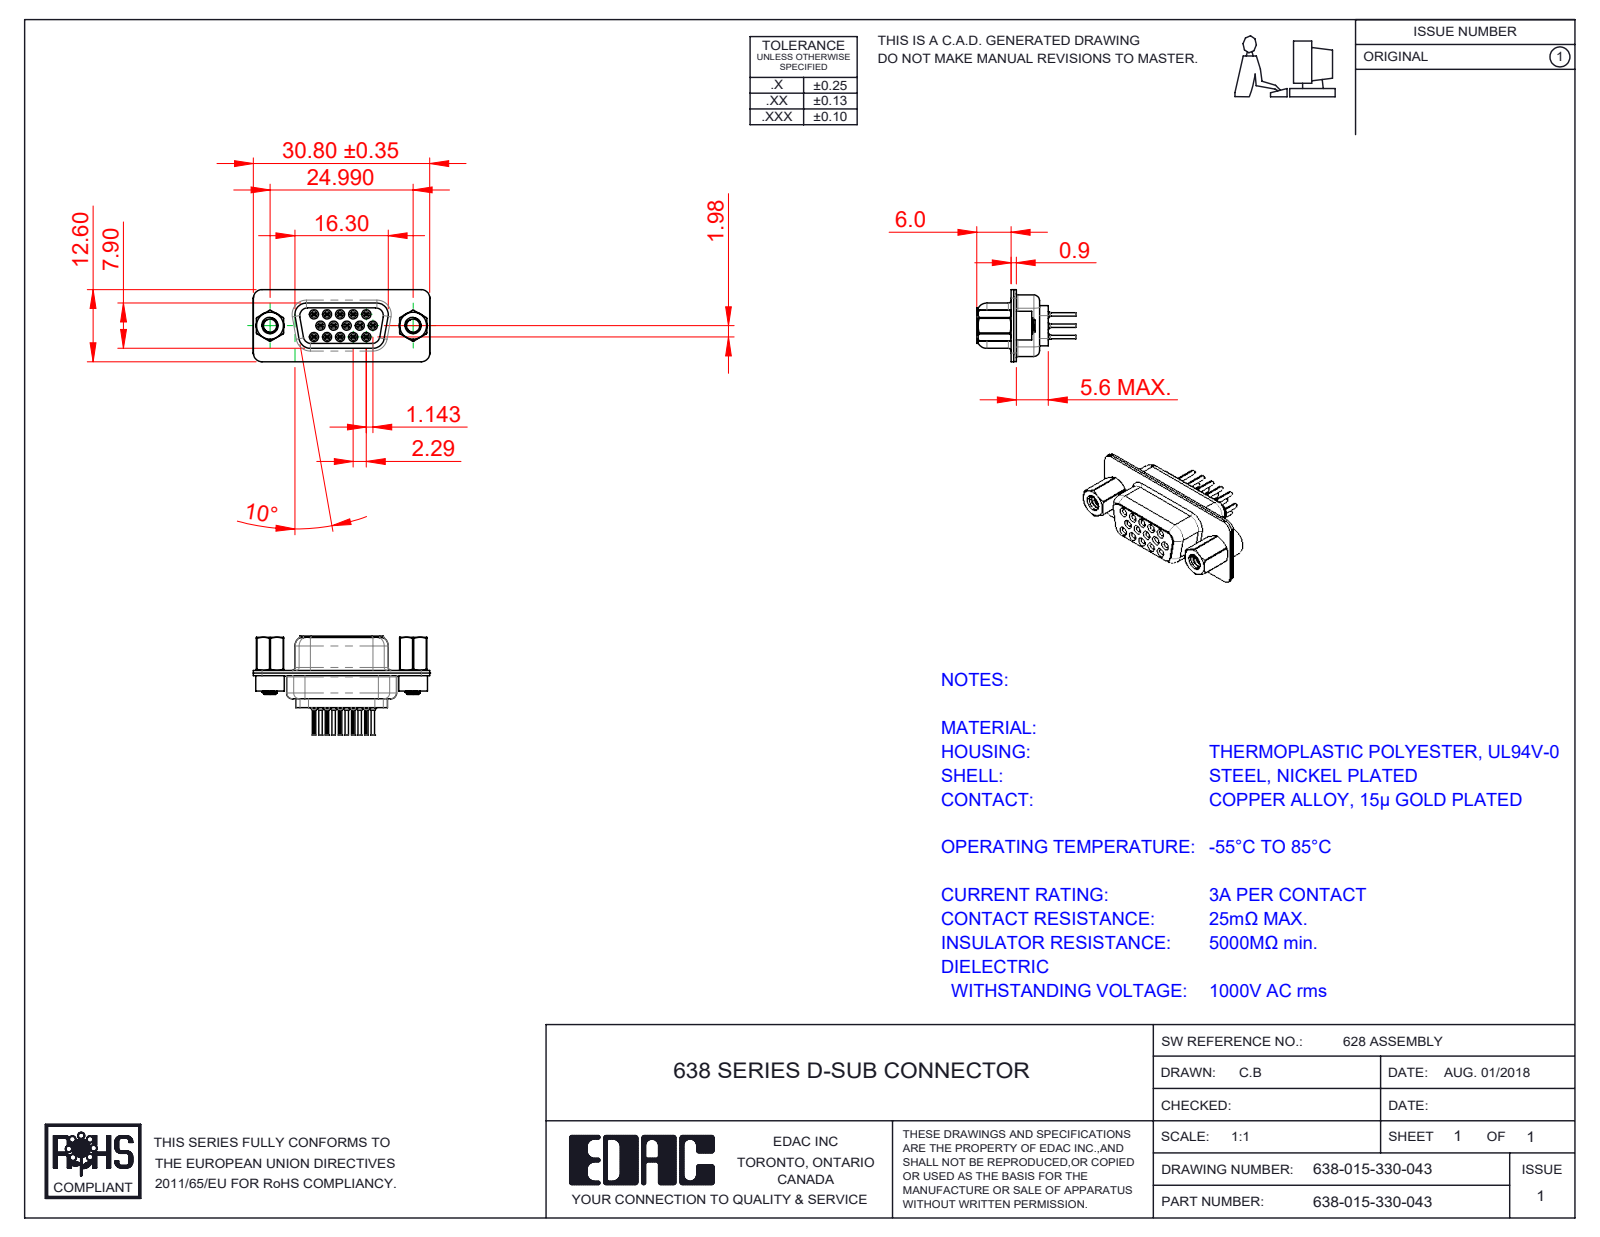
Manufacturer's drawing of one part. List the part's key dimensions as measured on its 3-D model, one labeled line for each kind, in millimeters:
Part name (STEP PRODUCT): 638 4-40 Hex Standoff; 638-015-330-043; 638 Housing_15 Contacts; 638 Contact Row 1_30 (+5 more)
STEP written by: SolidWorks 2020 (CONFIG_CONTROL_DESIGN)
Units: millimetres
Bodies: 22 solids, 2310 faces (554 planar, 704 cylindrical, 1052 other)
Overall size (bounding box): 30.81 × 17.3 × 12.6
Volume: 1 789 mm³ · Surface area: 6 081 mm²
Round holes (diameter × count): ⌀0.2 ×15, ⌀0.8 ×15, ⌀1 ×15, ⌀1.1 ×15, ⌀1.6 ×15, ⌀1.7 ×15, ⌀1.8 ×15, ⌀2 ×2, ⌀2.26 ×2, ⌀2.29 ×2, ⌀4 ×2, ⌀4.05 ×2
Round bosses / shafts (diameter × count): ⌀2 ×15, ⌀1.5 ×15, ⌀1.2 ×15, ⌀0.6 ×15, ⌀5 ×2, ⌀4.95 ×2, ⌀4.8 ×2, ⌀2.79 ×2
Partial cylindrical surfaces — rounded edges, fillets, slot ends (radius × count): R0.1 ×30, R1.5 ×20, R2 ×12, R0.28 ×10, R1.55 ×8, R1.35 ×5, R0.25 ×4, R0.5 ×4
Main face-to-face distances: 0.45, 0.9, 0.4, 1.43, 8.88, 6.6, 1.4, 2.28, 6.2, 0.85
Hole centre spacings: 3.96, 2.28, 4.57, 2.29, 6.05, 6.04, 6.86, 7.92
